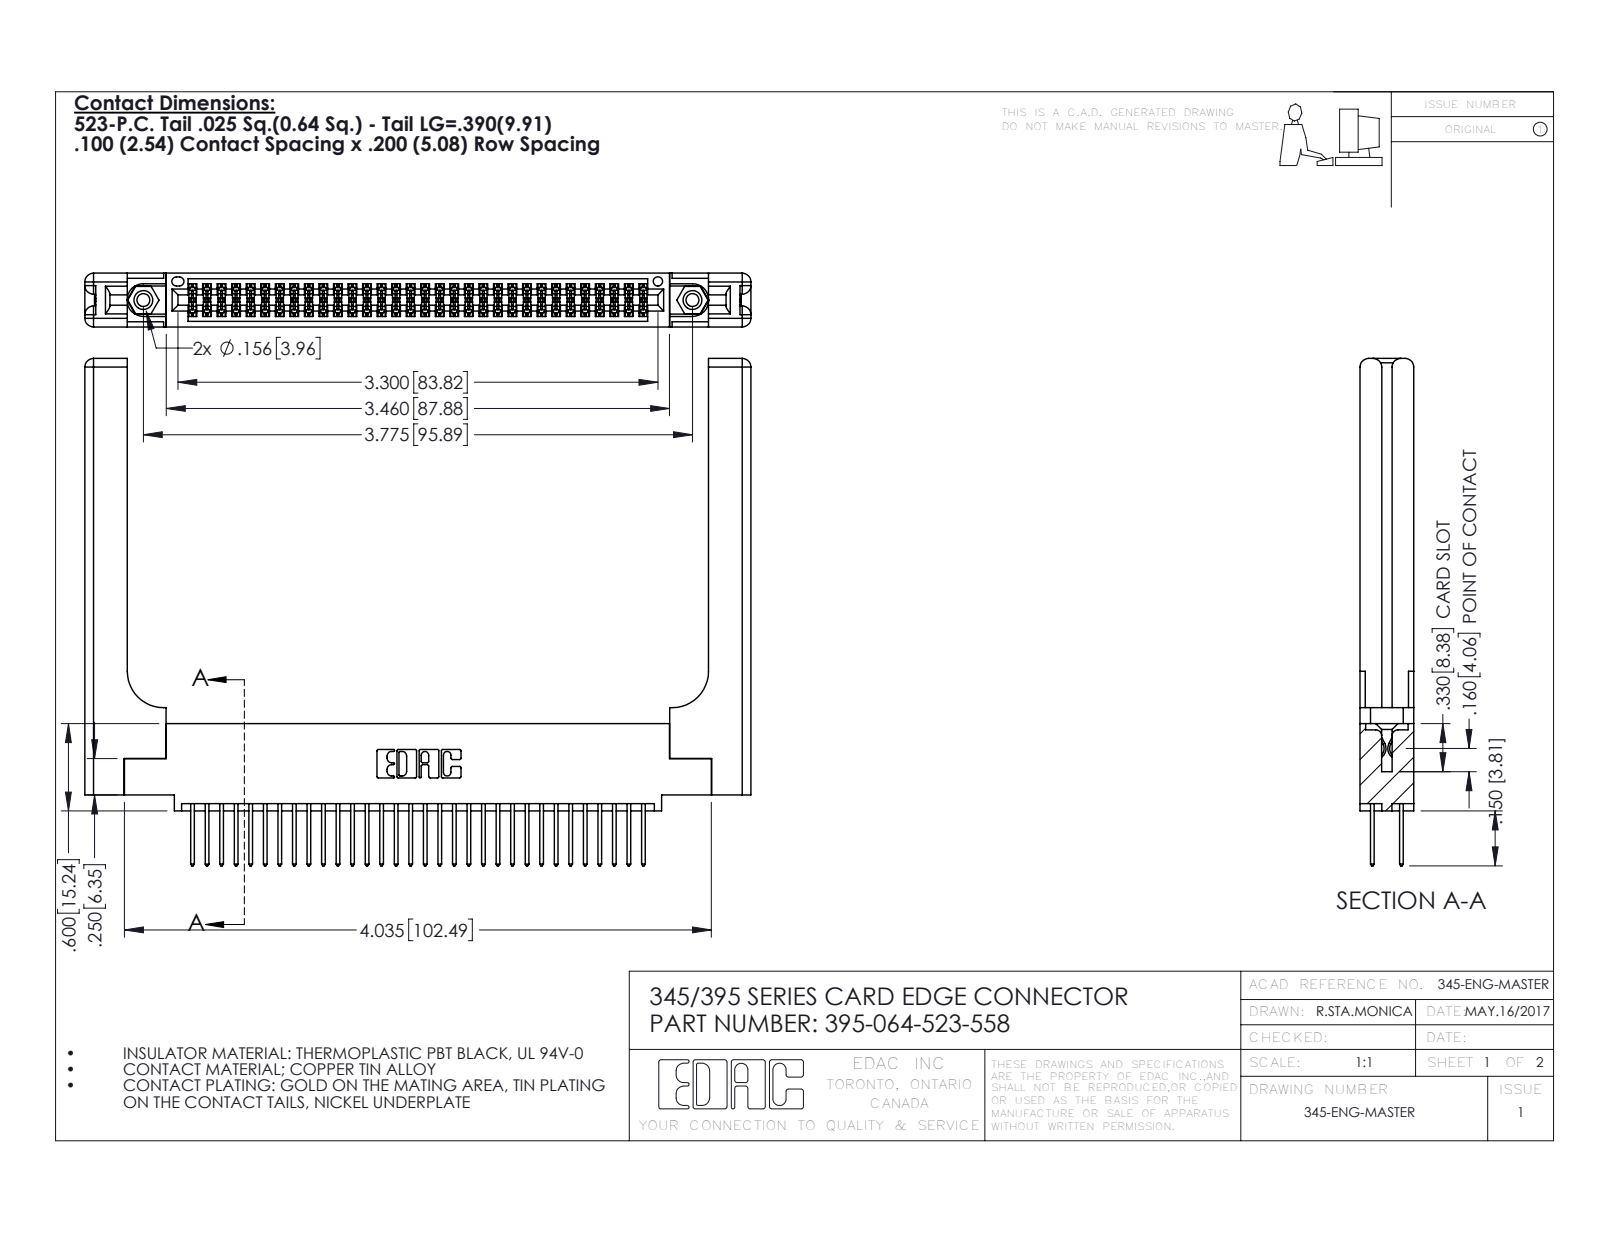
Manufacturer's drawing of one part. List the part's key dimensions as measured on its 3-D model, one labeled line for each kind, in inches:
Part name (STEP PRODUCT): 395-064-523-558; 345-292-001_345-293-123; 345 Part_0.110 Offset - 0.156 Dia-TH; 345-220-058_345-220-058 (+1 more)
STEP written by: SolidWorks 2016 (CONFIG_CONTROL_DESIGN)
Units: inches
Bodies: 69 solids, 3586 faces (2344 planar, 1182 cylindrical, 60 other)
Overall size (bounding box): 4.579 × 3.487 × 0.37
Volume: 1.205 in³ · Surface area: 34.4 in²
Round holes (diameter × count): ⌀0.089 ×2, ⌀0.125 ×2, ⌀0.156 ×2, ⌀0.064 ×1
Round bosses / shafts (diameter × count): ⌀0.155 ×2
Partial cylindrical surfaces — rounded edges, fillets, slot ends (radius × count): R0.006 ×96, R0.01 ×64, R0.01 ×22, R0.06 ×16, R0.007 ×6, R0.031 ×6, R0.026 ×3, R0.014 ×2
Main face-to-face distances: 0.072, 0.298, 0.37, 0.098, 0.272, 0.025, 0.2, 0.225, 0.148, 0.15
Hole centre spacings: 0.27, 3.54, 3.775
